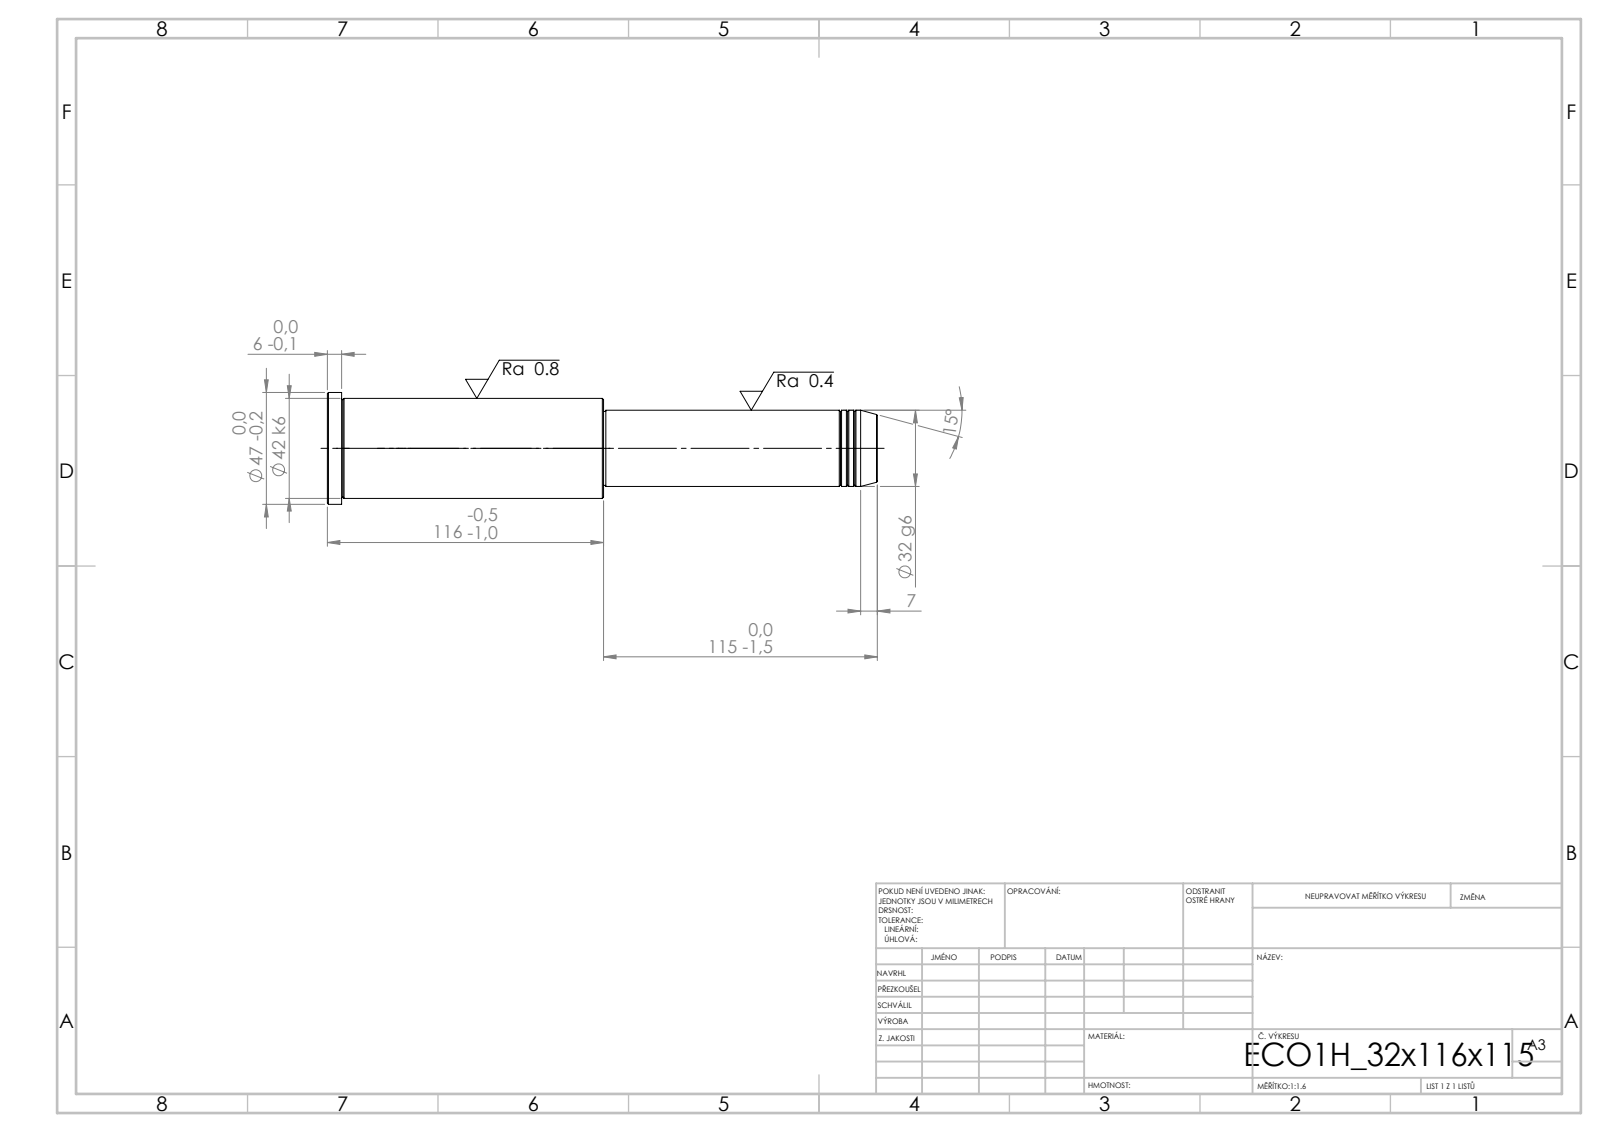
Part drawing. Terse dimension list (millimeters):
written by: SolidWorks 2019 (CONFIG_CONTROL_DESIGN)
unit: mm
bodies: 1 solid, 43 faces (5 planar, 14 cylindrical, 24 other)
size: 231 × 47 × 47
volume: 254 408 mm³; area: 30 474 mm²
bosses: 1× ⌀47, 1× ⌀42, 1× ⌀32, 1× ⌀31
face distances: 231, 115, 116, 225, 110, 6, 114, 1, 111, 117
